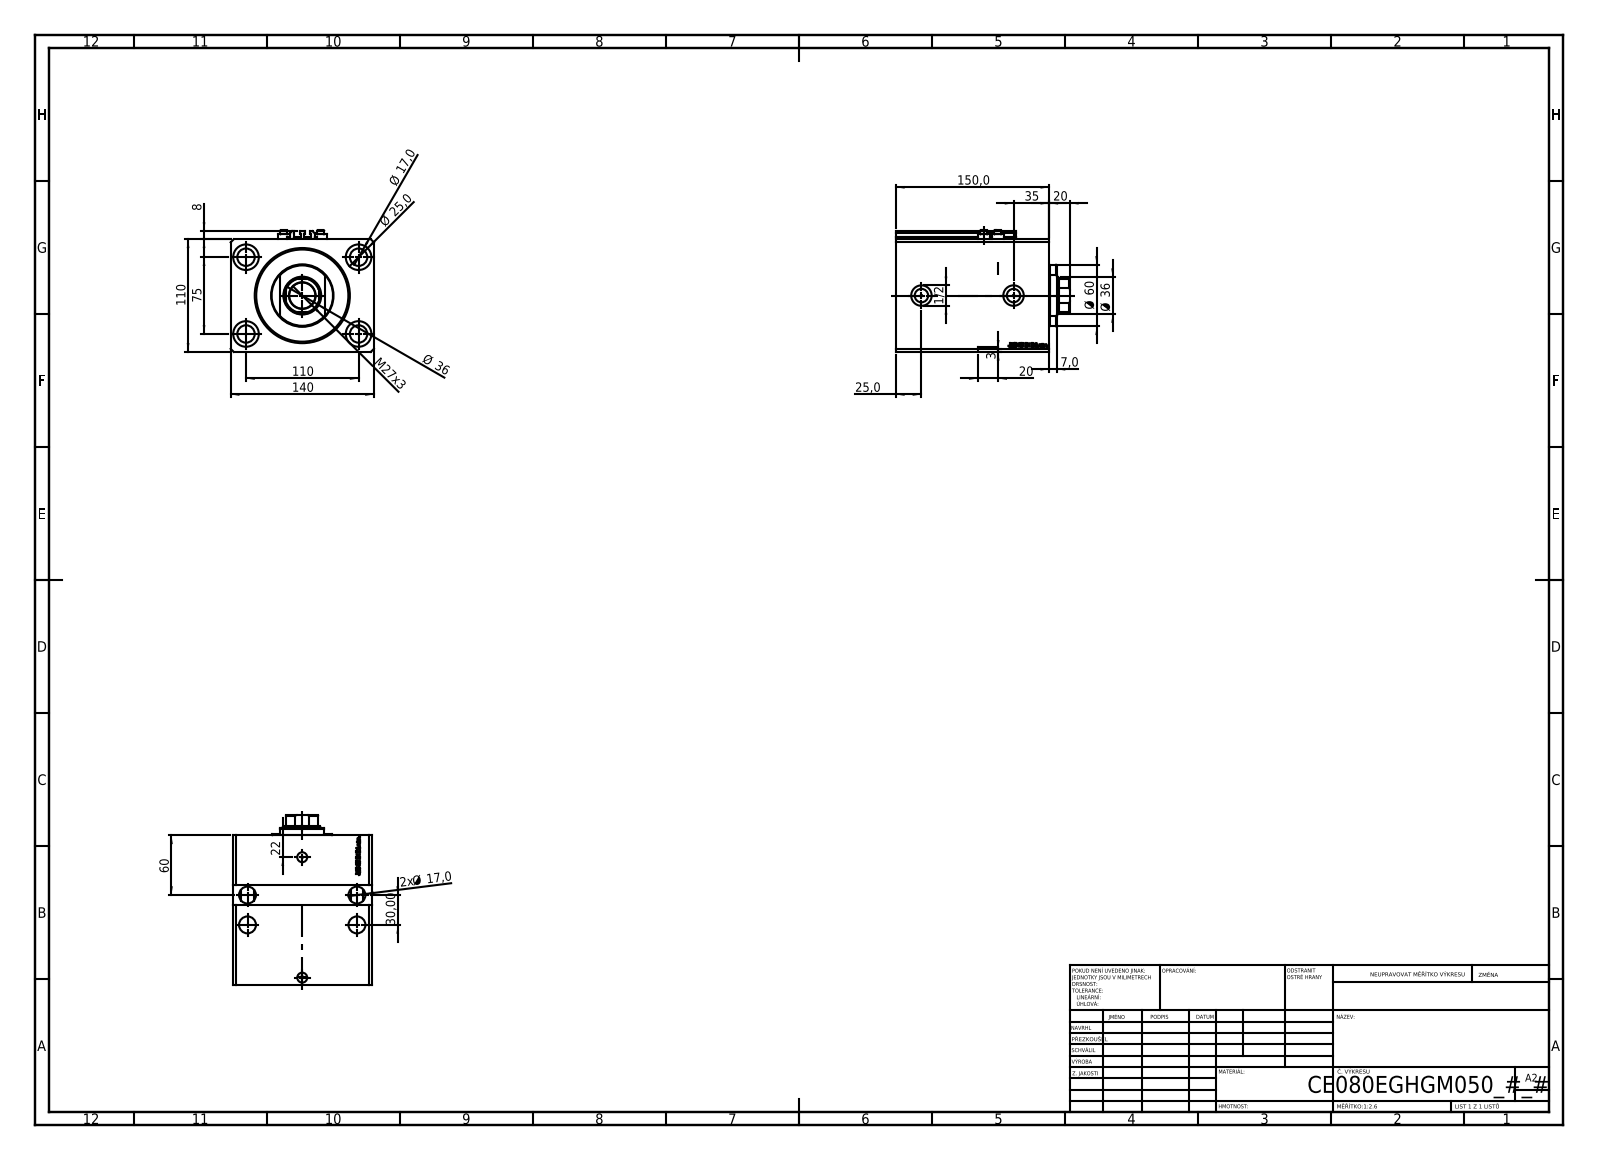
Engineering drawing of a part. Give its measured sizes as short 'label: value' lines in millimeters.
name: V250CE_C_VCP; ALLEN BOLT V250CE; V250CE_VC_E; V250CE_E_Body
written by: SolidWorks 2019 (CONFIG_CONTROL_DESIGN)
unit: mm
bodies: 8 solids, 1132 faces (548 planar, 146 cylindrical, 438 other)
size: 170 × 140 × 119
volume: 1 872 000 mm³; area: 258 640 mm²
holes: 8× ⌀17, 4× ⌀1.25, 4× ⌀4, 4× ⌀25, 2× ⌀10, 2× ⌀13.16, 2× ⌀20, 1× ⌀25.5, 1× ⌀36, 1× ⌀80, 1× ⌀93
bosses: 4× ⌀11.6, 4× ⌀7, 1× ⌀60
rounds: 10× R0.2, 1× R17.5
face distances: 110, 140, 150, 25, 125, 105, 20, 130, 50, 70
hole spacings: 66.57, 110, 13.6, 30, 33.62, 36, 37.22, 38.23
